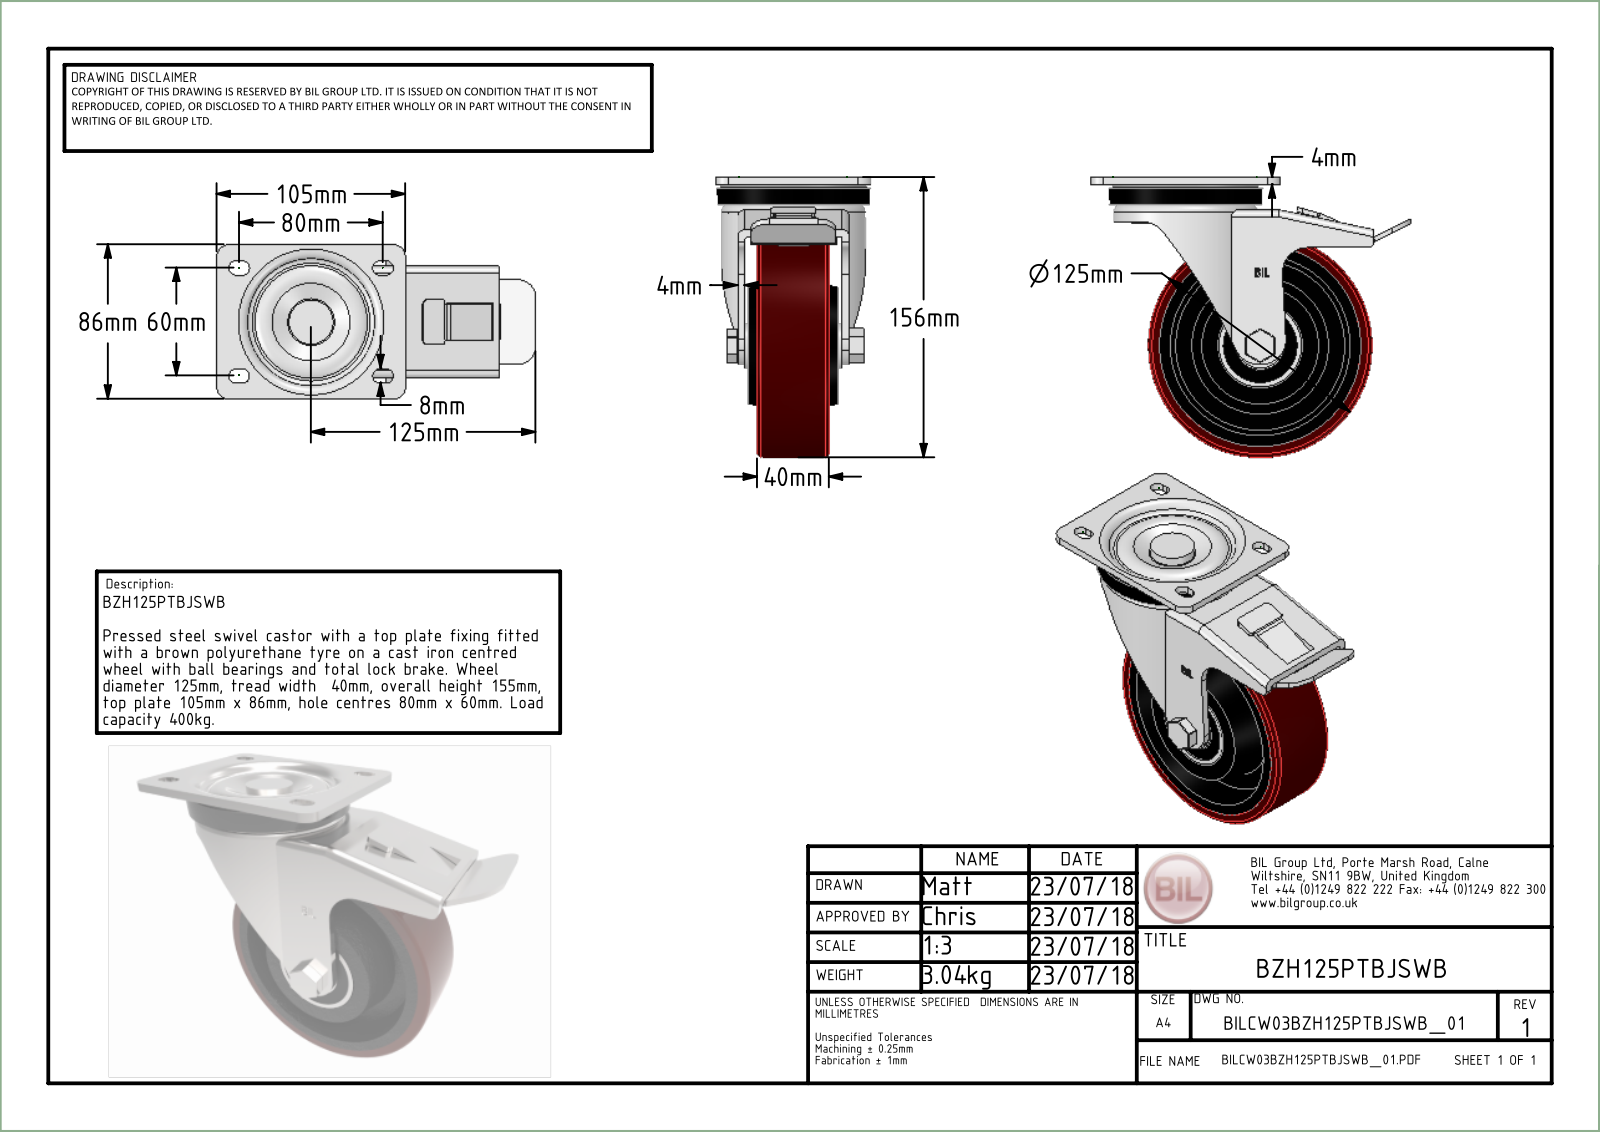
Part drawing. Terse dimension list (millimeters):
name: BZH125PTBJSWB v3; BZH125ASSWB - 52 v1; BZH125ASSWB v1 (1); ZINC PLATED, PRESSED STEEL TOP PLATE (1) (+8 more)
written by: Autodesk Translation Framework v14.10.0.0 (AUTOMOTIVE_DESIGN)
unit: mm
bodies: 40 solids, 1324 faces (624 planar, 260 cylindrical, 440 other)
size: 177.5 × 155 × 86
volume: 503 945 mm³; area: 221 522 mm²
holes: 1× ⌀6, 1× ⌀10, 1× ⌀10.2, 1× ⌀10.5, 1× ⌀12, 1× ⌀20, 1× ⌀25, 1× ⌀28.5, 1× ⌀30.8, 1× ⌀32, 1× ⌀40.3, 1× ⌀40.5
bosses: 1× ⌀80, 1× ⌀62, 1× ⌀60, 1× ⌀40.8, 1× ⌀31.3, 1× ⌀31, 1× ⌀27, 1× ⌀25
rounds: 19× R0.5, 14× R0.75, 8× R1.5, 8× R2, 8× R4.5, 6× R3, 4× R4, 4× R8
face distances: 4, 5, 22, 1, 50, 6, 24, 16, 10, 7.5
